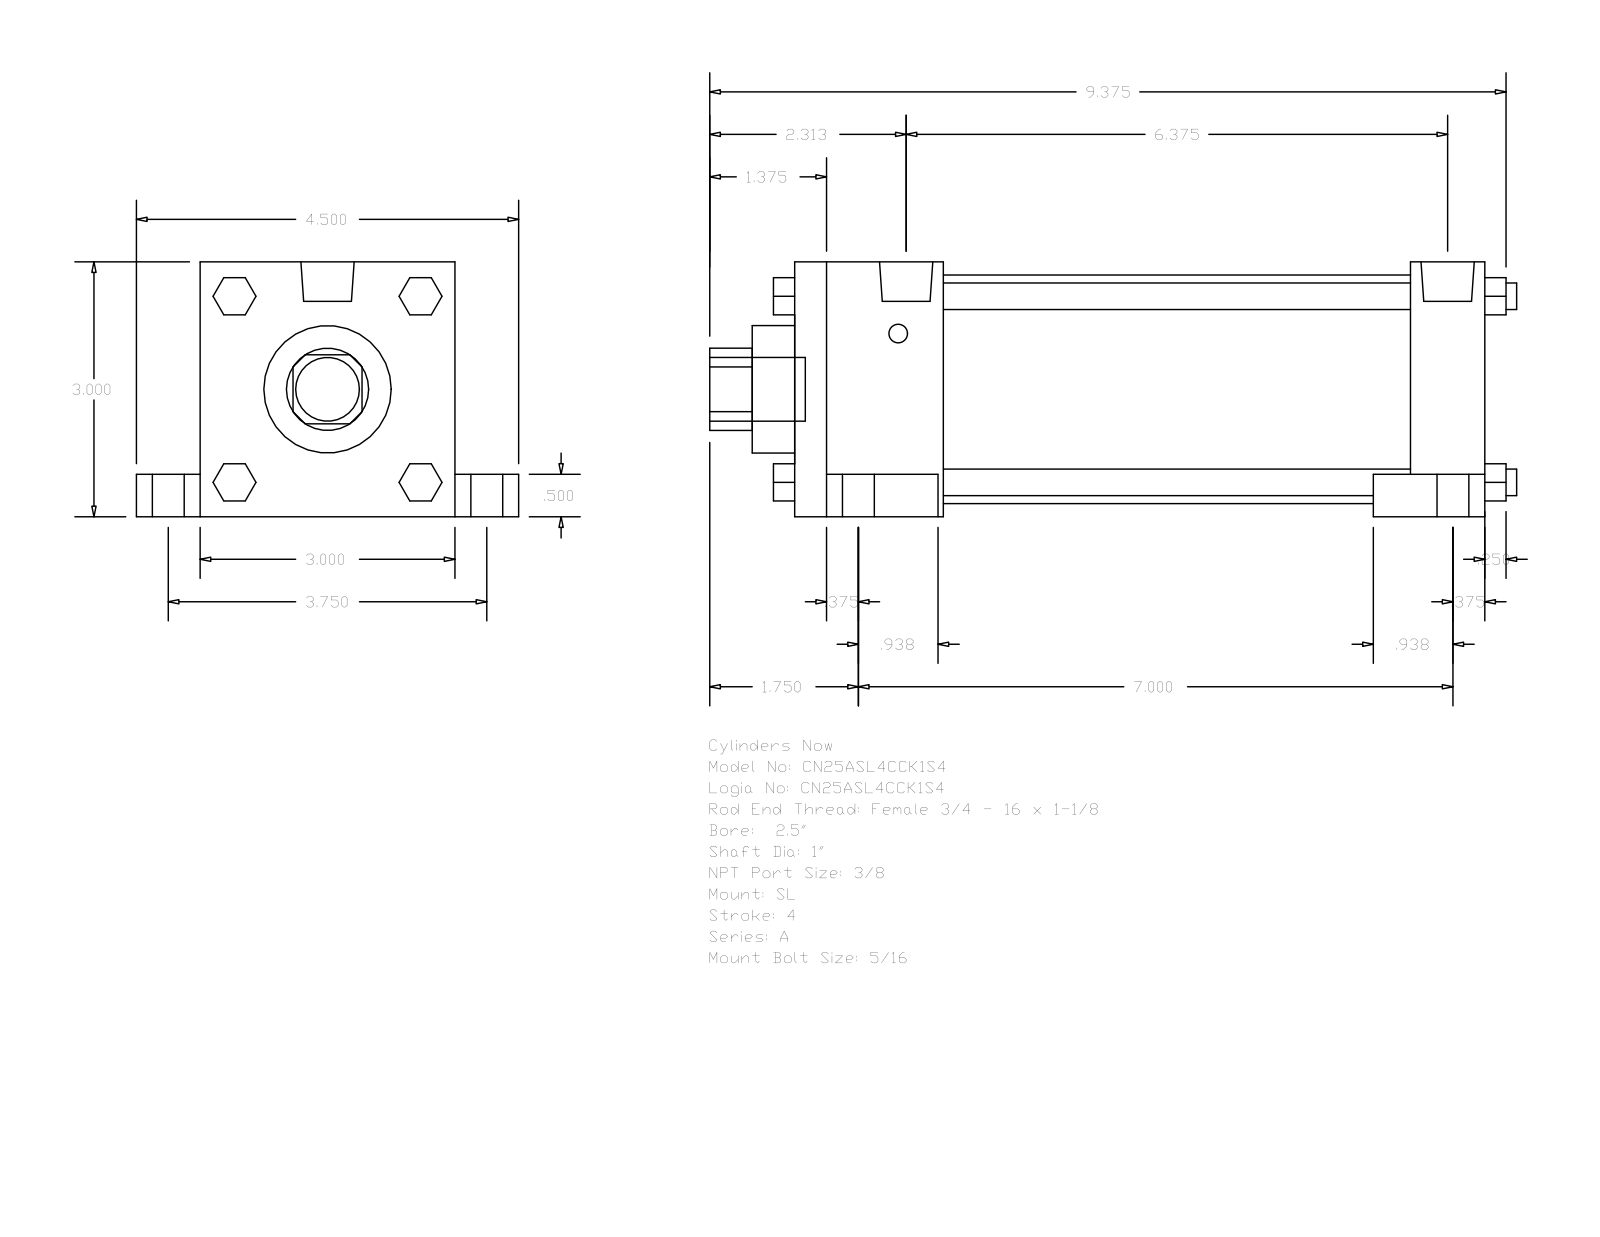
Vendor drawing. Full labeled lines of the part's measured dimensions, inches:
Part name (STEP PRODUCT): A_SL__0250_1
STEP written by: GSSL Pune (CONFIG_CONTROL_DESIGN)
Units: inches
Bodies: 0 solids, 148 faces (112 planar, 36 cylindrical, 0 other)
Overall size (bounding box): 9.5 × 4.5 × 3
Round holes (diameter × count): ⌀1 ×1, ⌀1.5 ×1, ⌀2.69 ×1
Round bosses / shafts (diameter × count): ⌀0.625 ×4, ⌀0.375 ×4, ⌀0.313 ×4, ⌀0.219 ×4, ⌀0.627 ×2, ⌀0.75 ×1
Partial cylindrical surfaces — rounded edges, fillets, slot ends (radius × count): R0.484 ×1
Main face-to-face distances: 3, 8.125, 0.5, 1.75, 6.375, 7.25, 5.5, 0.875, 0.75, 2.5
